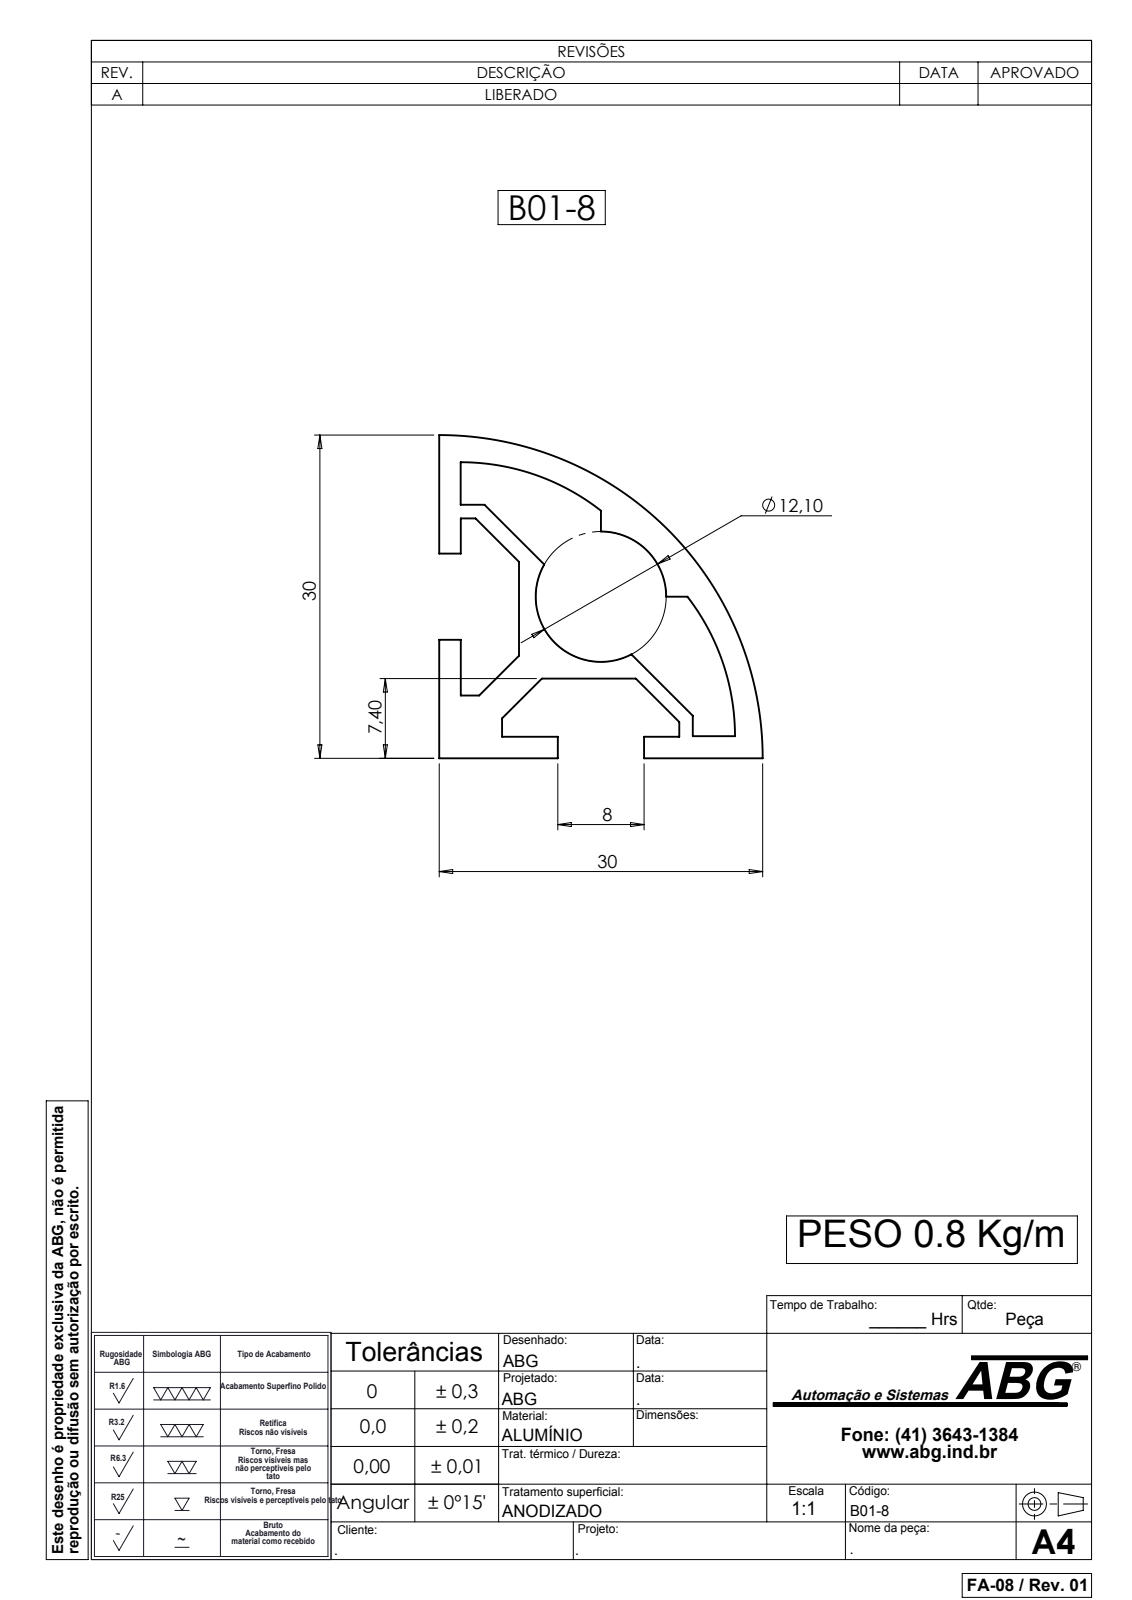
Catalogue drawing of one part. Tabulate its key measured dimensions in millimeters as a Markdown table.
| quantity | value |
| --- | --- |
| part name | B01-8 |
| STEP written by | SolidWorks 2007 (CONFIG_CONTROL_DESIGN) |
| units | millimeters |
| bodies | 1 solid, 37 faces (32 planar, 5 cylindrical, 0 other) |
| overall size | 6000 × 30 × 30 |
| volume | 1 677 000 mm³ |
| surface area | 1 478 000 mm² |
| partial cylindrical surfaces (radius × count) | 6.05 × 1, 21.06 × 1, 21.2 × 1, 30 × 1 |
| main face-to-face distances | 7.4, 2, 5.4, 1.3, 1.49, 4, 3, 21.53, 11, 9 |
